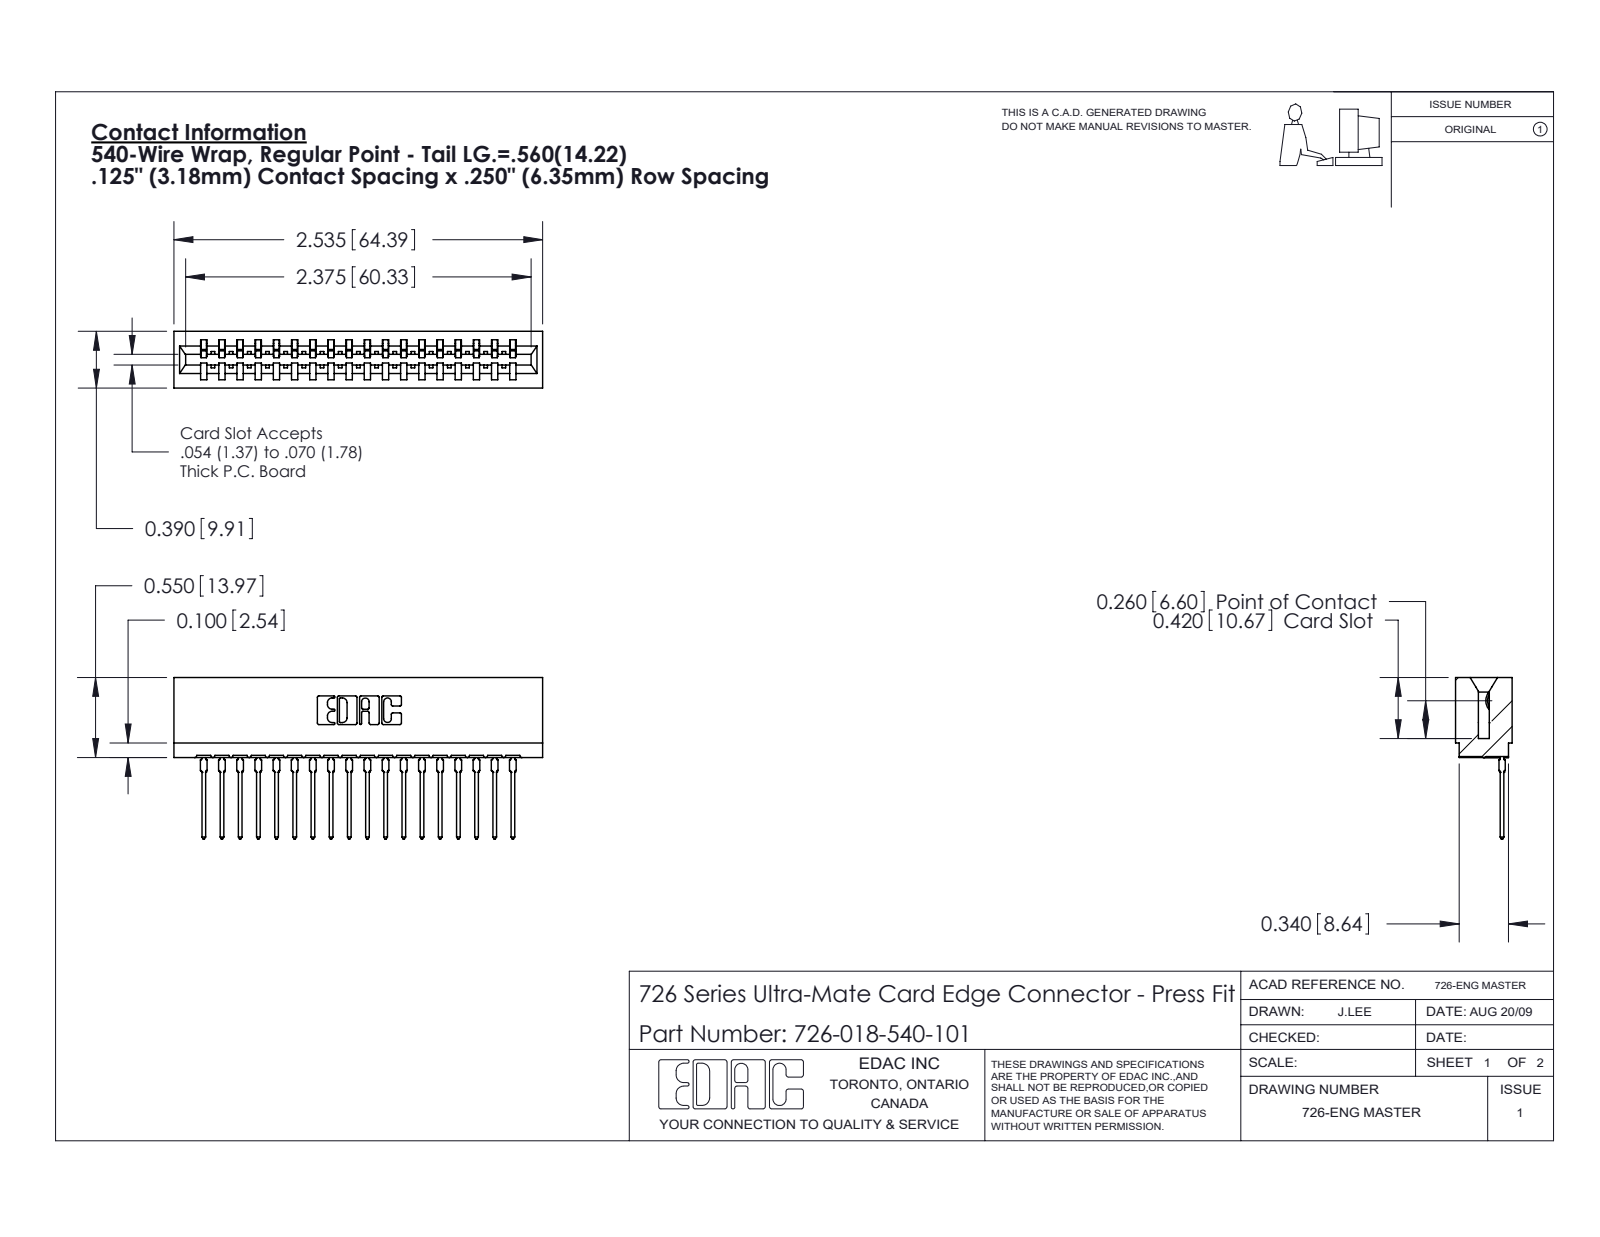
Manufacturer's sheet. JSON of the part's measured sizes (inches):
{"part_name": "726 Part_.515 Slot Depth - 01; 726-018-540-101; 746-292-001_540", "step_written_by": "SolidWorks 2020 (CONFIG_CONTROL_DESIGN)", "units": "inches", "bodies": {"solids": 19, "faces": 2041, "planar": 1189, "cylindrical": 384, "other": 468}, "overall_size": [2.535, 1.109, 0.39], "volume_in3": 0.362, "surface_area_in2": 13.81, "partial_cylinders_radius": [[0.021, 36], [0.01, 22], [0.015, 19], [0.007, 6], [0.031, 6], [0.005, 4], [0.011, 4], [0.026, 3]], "face_to_face_distances": [0.057, 0.333, 0.39, 0.25, 0.025, 0.307, 0.083, 0.75, 0.5, 0.125]}
